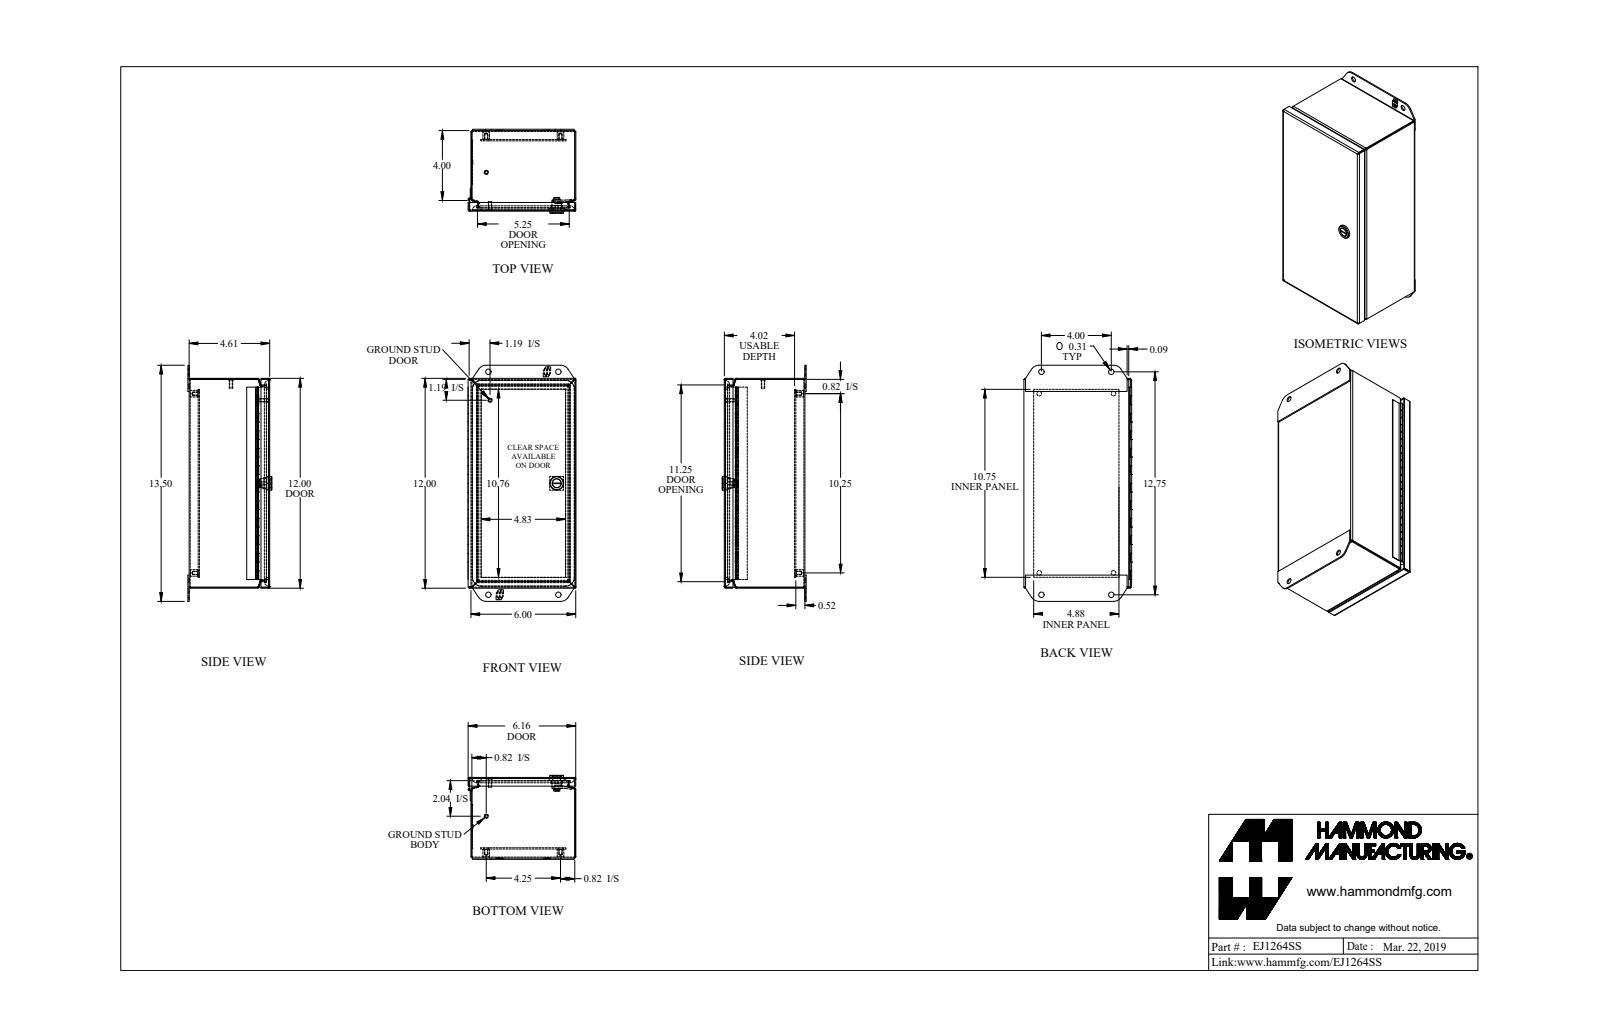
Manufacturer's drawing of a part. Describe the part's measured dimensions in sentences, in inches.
The part is named "EJ1264SS_Default". Its 3-D file was written by "SolidWorks 2019 (CONFIG_CONTROL_DESIGN)". It is 16 solids with 720 faces: 402 planar, 222 cylindrical and 96 other. Overall it measures 13.5 by 6.165 by 4.805 inches. Its volume is 27.59 cubic inches and its surface area 913.3 square inches. Round holes: 4 of diameter 0.156, 4 of diameter 0.265, 4 of diameter 0.313, 1 of diameter 0.05, 1 of diameter 0.516. Round bosses or shafts: 4 of diameter 0.375, 2 of diameter 0.25, 2 of diameter 0.19, 1 of diameter 0.788, 1 of diameter 0.535, 1 of diameter 0.496, 1 of diameter 0.435, 1 of diameter 0.1. Partial cylindrical surfaces (rounded edges, fillets, slot ends): 16 of radius 0.029, 16 of radius 0.086, 12 of radius 0.281, 4 of radius 0.25, 4 of radius 0.499, 4 of radius 0.5, 2 of radius 0.06, 1 of radius 0.03. The main face-to-face distances are 0.057, 4.554, 5.943, 4.611, 4.497, 0.072, 0.589, 4.094, 4.037, 0.46. The hole center spacings are 1.256, 4.31, 11.501, 12.218, 4, 4.25, 5.13, 6.376.
